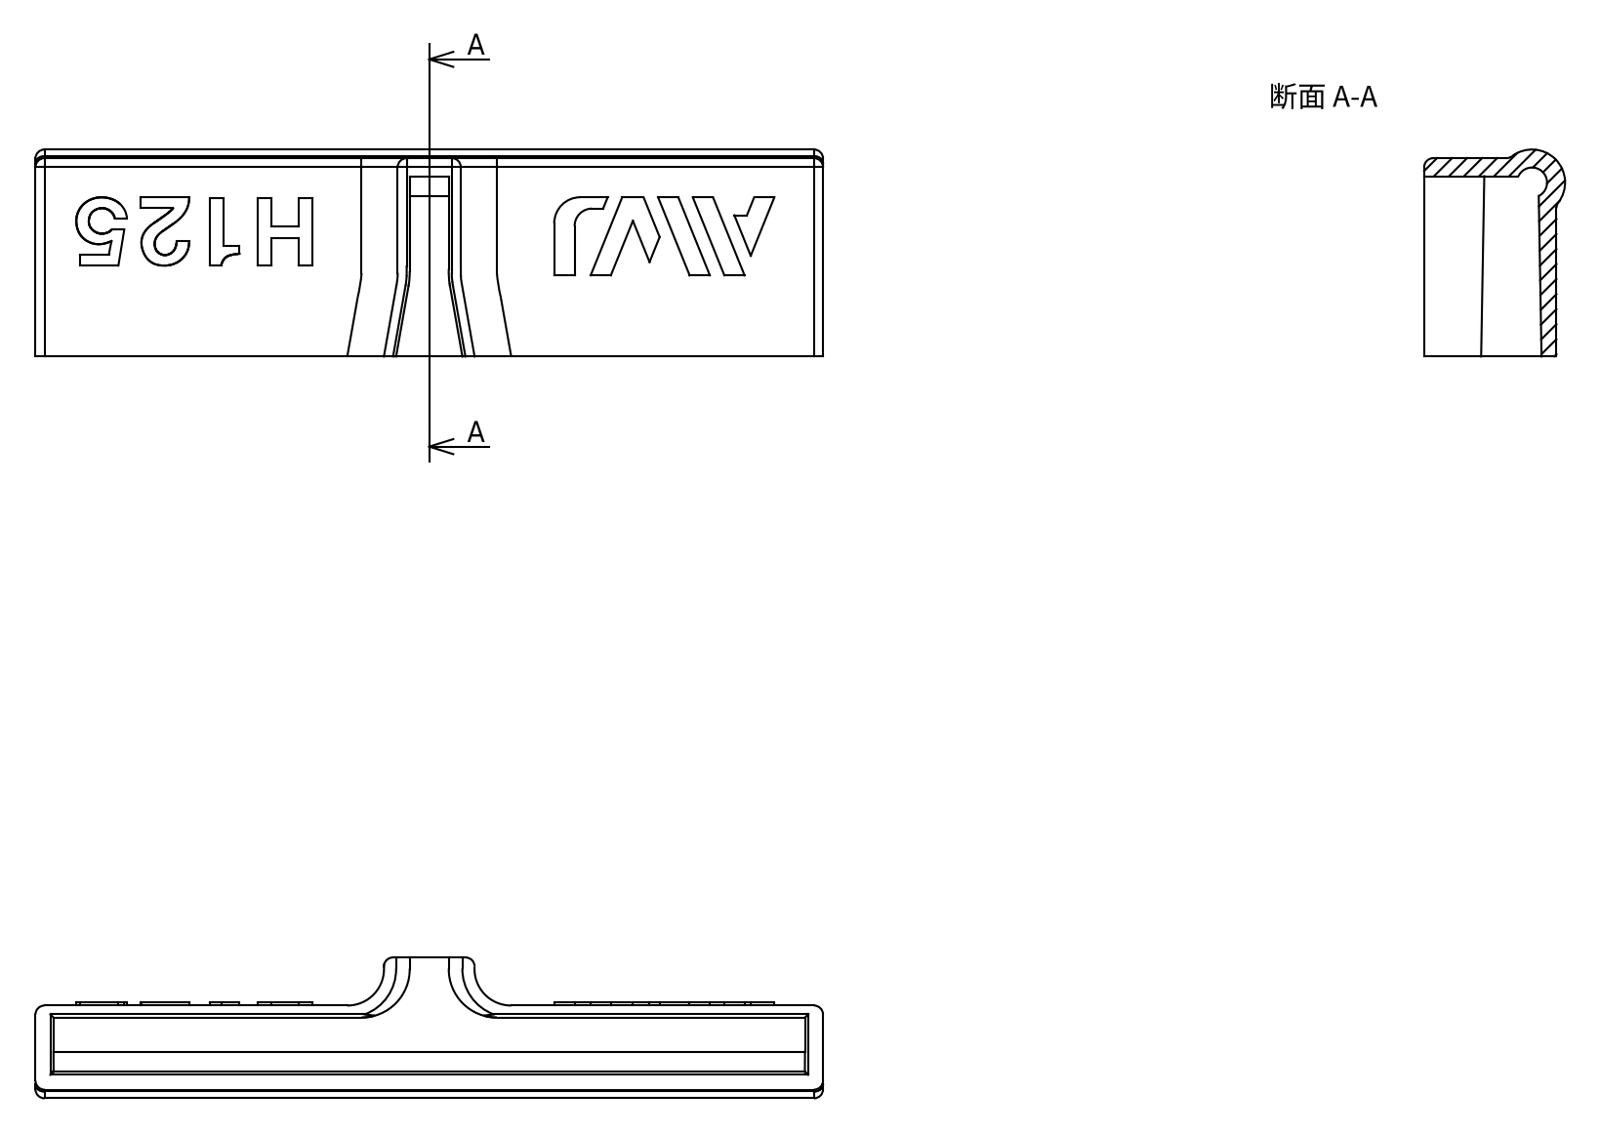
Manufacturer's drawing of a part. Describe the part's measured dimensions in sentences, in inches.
Its 3-D file was written by "Spatial InterOp 3D (CONFIG_CONTROL_DESIGN)". It is 6 solids with 132 faces: 83 planar, 17 cylindrical and 32 other. Overall it measures 5.157 by 1.397 by 0.923 inches. Its volume is 1.595 cubic inches and its surface area 35.17 square inches. Partial cylindrical surfaces (rounded edges, fillets, slot ends): 10 of radius 0.059, 1 of radius 0.098, 1 of radius 0.114, 1 of radius 0.17, 1 of radius 0.217. The main face-to-face distances are 0.551, 0.118, 1.181, 1.299, 0.571, 0.02, 5.157, 0.123, 0.211, 0.086.
